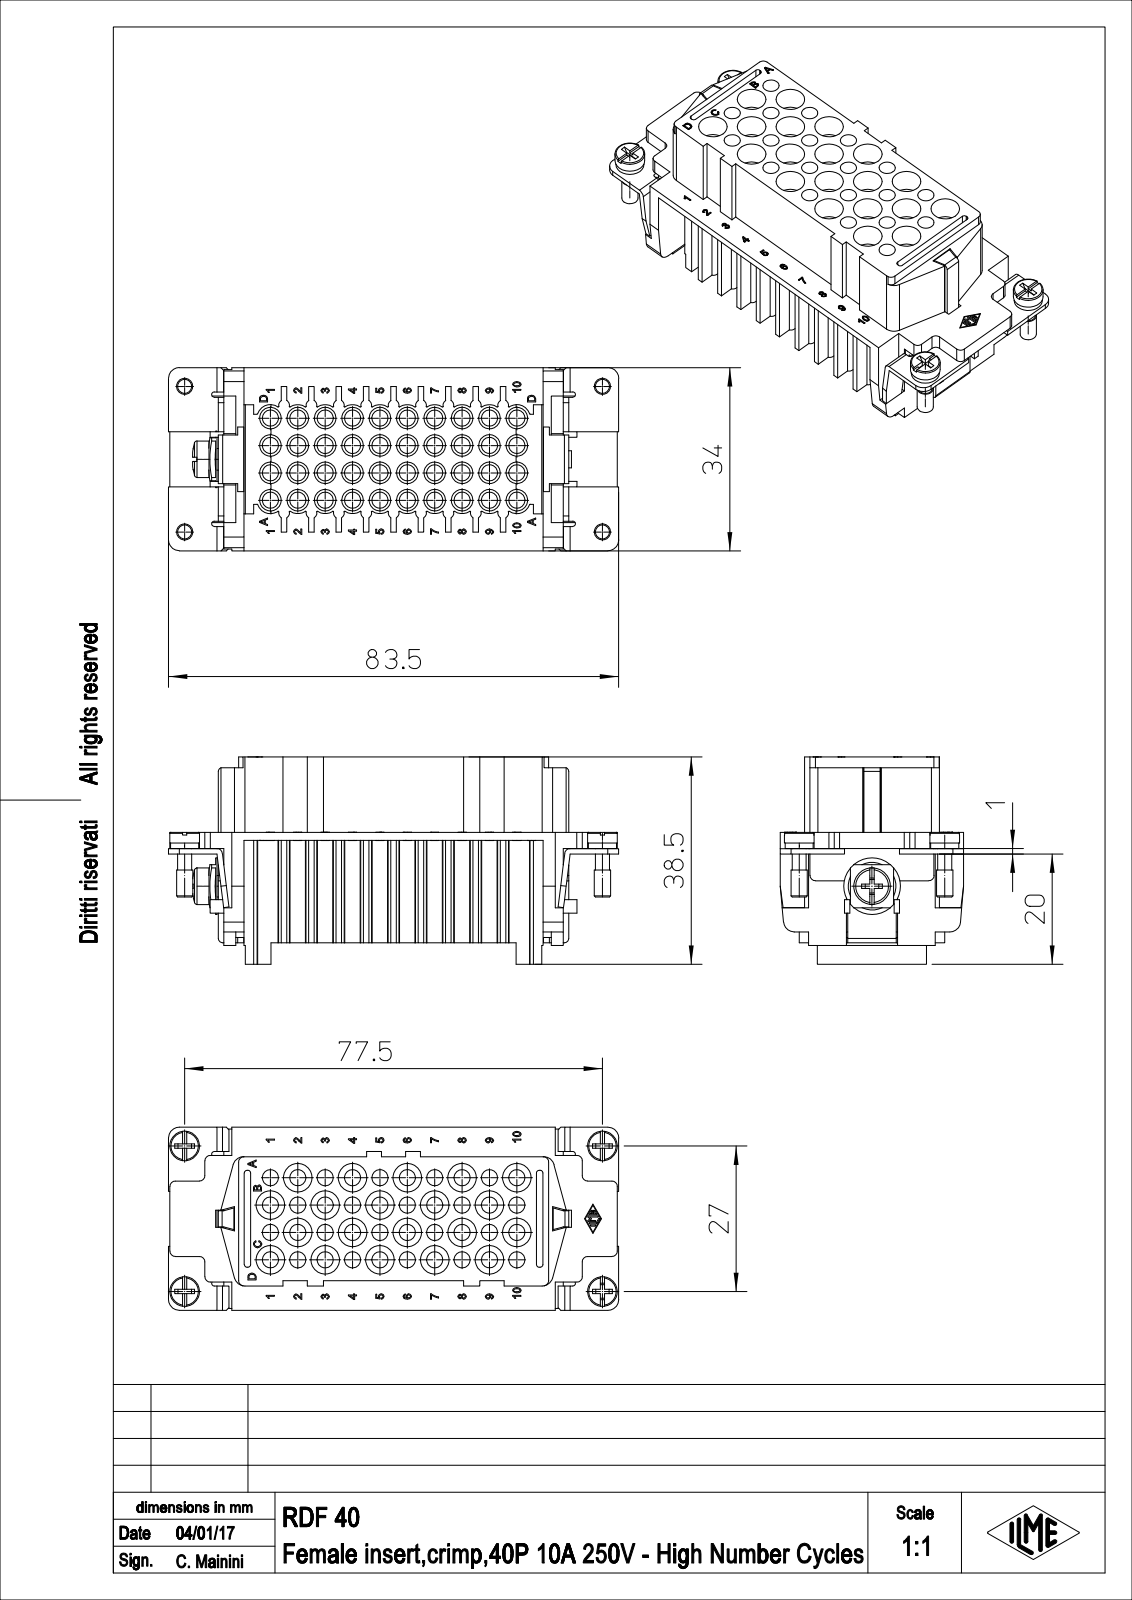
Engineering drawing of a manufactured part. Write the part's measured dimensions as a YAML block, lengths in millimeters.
part_name: "RDF_40"
step_written_by: "PTC Creo Elements/Direct Modeling 19.0E 27-Jun-2016 (C) Parametric Technology GmbH (AUTOMOTIVE_DESIGN)"
units: millimeters
bodies: {solids: 1, faces: 1683, planar: 819, cylindrical: 410, other: 454}
overall_size: [83.5, 38.51, 34]
volume: 36200
surface_area: 35895
round_holes:
  - {diameter: 3, count: 40}
  - {diameter: 4, count: 40}
  - {diameter: 5.3, count: 20}
  - {diameter: 2.46, count: 4}
round_bosses_or_shafts:
  - {diameter: 5.5, count: 4}
  - {diameter: 5.2, count: 4}
  - {diameter: 3, count: 4}
  - {diameter: 2.6, count: 4}
  - {diameter: 10.5, count: 1}
  - {diameter: 6.8, count: 1}
  - {diameter: 6, count: 1}
  - {diameter: 4, count: 1}
partial_cylinders:
  - {radius: 0.1, count: 40}
  - {radius: 1, count: 38}
  - {radius: 2.5, count: 20}
  - {radius: 0.5, count: 12}
  - {radius: 2, count: 10}
  - {radius: 0.7, count: 2}
  - {radius: 0.8, count: 2}
face_to_face_distances: [1.5, 1, 15.5, 59.25, 14, 3.5, 2.25, 23, 20.5, 19]
hole_center_spacings: [11.36, 5.08, 16.06, 7.18, 10.16, 18.32, 15.24, 20.95]
